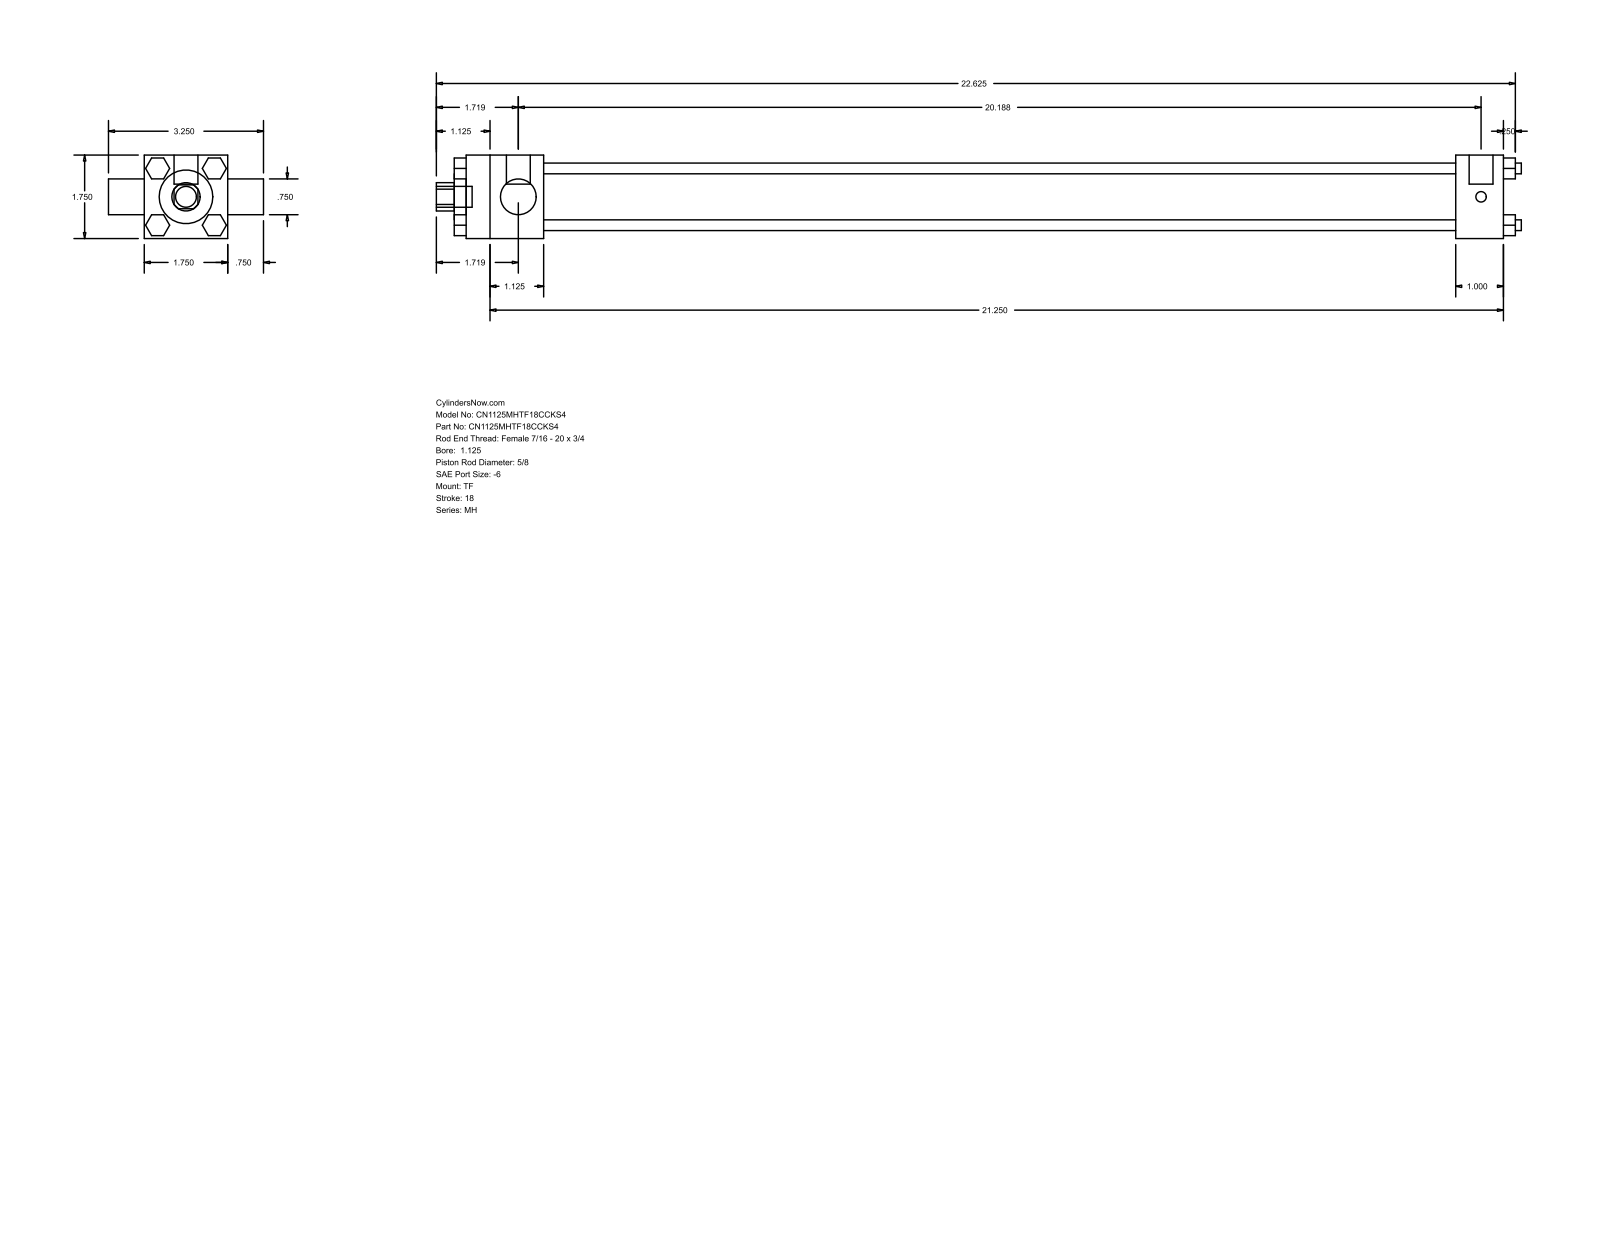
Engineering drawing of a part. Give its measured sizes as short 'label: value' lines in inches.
name: MH_TF__0112_0.625
written by: GSSL Pune (CONFIG_CONTROL_DESIGN)
unit: in
bodies: 0 solids, 120 faces (92 planar, 28 cylindrical, 0 other)
size: 22.75 × 3.25 × 1.75
holes: 1× ⌀0.625, 1× ⌀0.75, 1× ⌀1.125, 1× ⌀1.375
bosses: 4× ⌀0.225, 3× ⌀0.219, 2× ⌀0.5, 1× ⌀0.437
rounds: 1× R0.297
face distances: 1.75, 0.437, 19.125, 20.125, 1, 1.625, 20.75, 21.75, 1.875, 22
